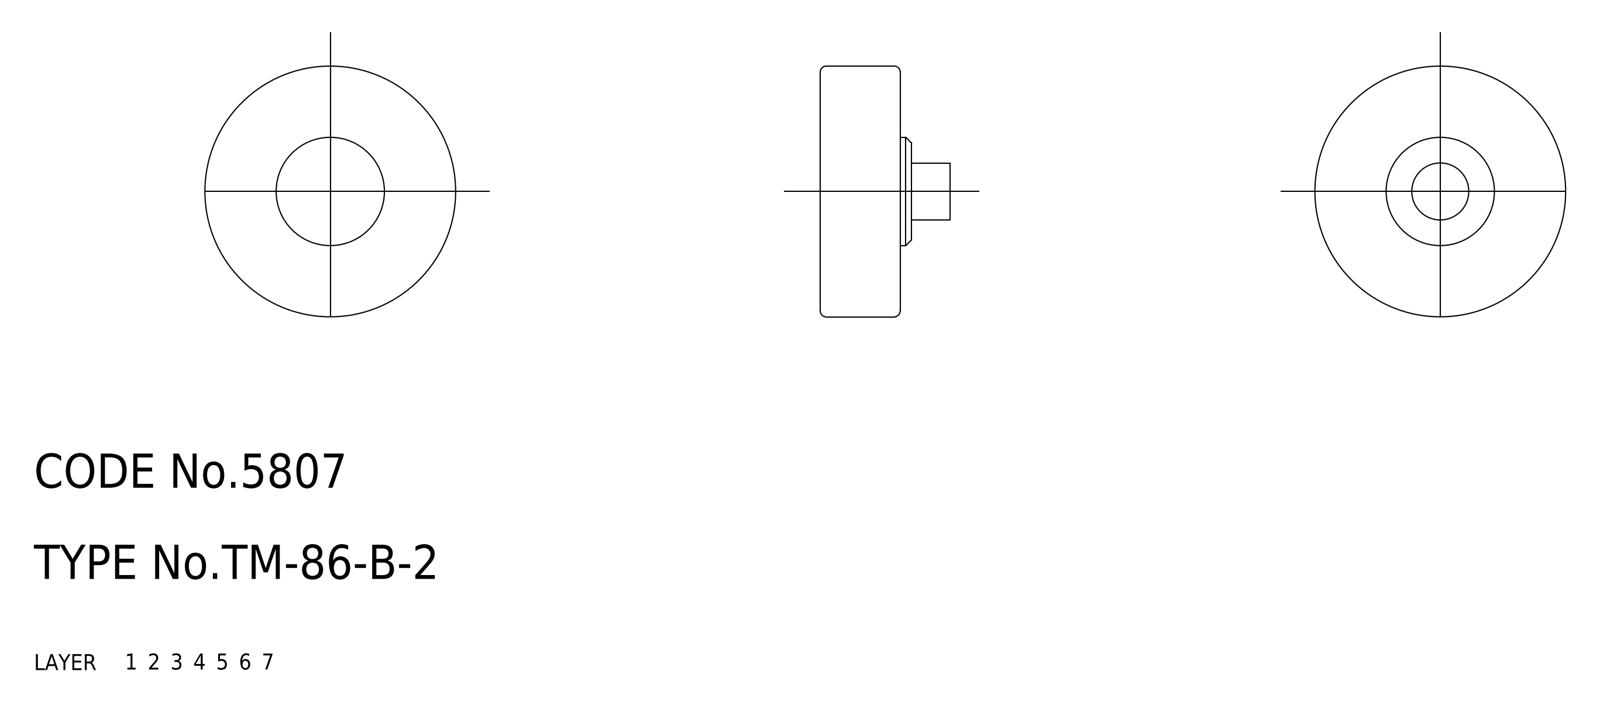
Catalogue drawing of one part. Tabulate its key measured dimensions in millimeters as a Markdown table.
| quantity | value |
| --- | --- |
| part name | roller |
| STEP written by | CADfix (AUTOMOTIVE_DESIGN) |
| units | millimeters |
| bodies | 1 solid, 30 faces (0 planar, 0 cylindrical, 30 other) |
| overall size | 22 × 22 × 11.4 |
| volume | 2 782 mm³ |
| surface area | 1 795 mm² |
